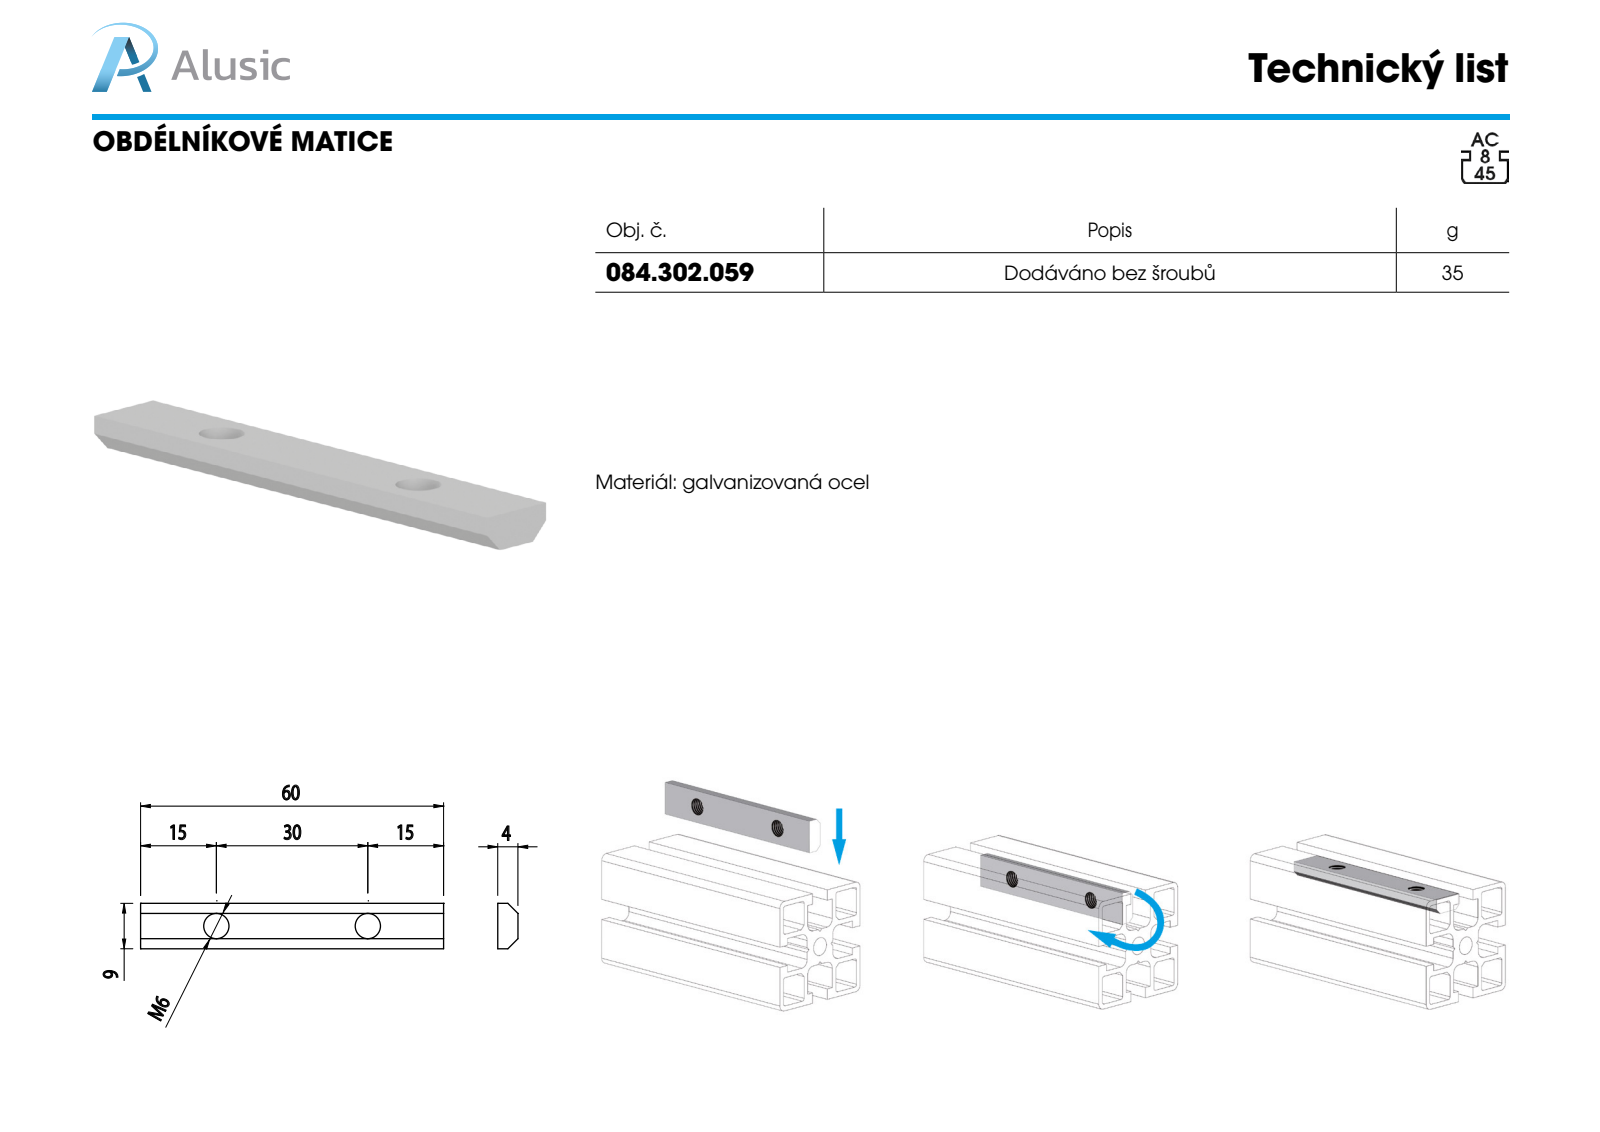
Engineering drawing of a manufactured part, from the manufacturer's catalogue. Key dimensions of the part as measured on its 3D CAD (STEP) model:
Part name (STEP PRODUCT): 084.302.059
STEP written by: SolidWorks 2012 (CONFIG_CONTROL_DESIGN)
Units: millimetres
Bodies: 1 solid, 14 faces (10 planar, 4 cylindrical, 0 other)
Overall size (bounding box): 60 × 9 × 4
Volume: 1 763 mm³ · Surface area: 1 531 mm²
Round holes (diameter × count): ⌀5 ×2
Main face-to-face distances: 4, 9, 60
Hole centre spacings: 30
